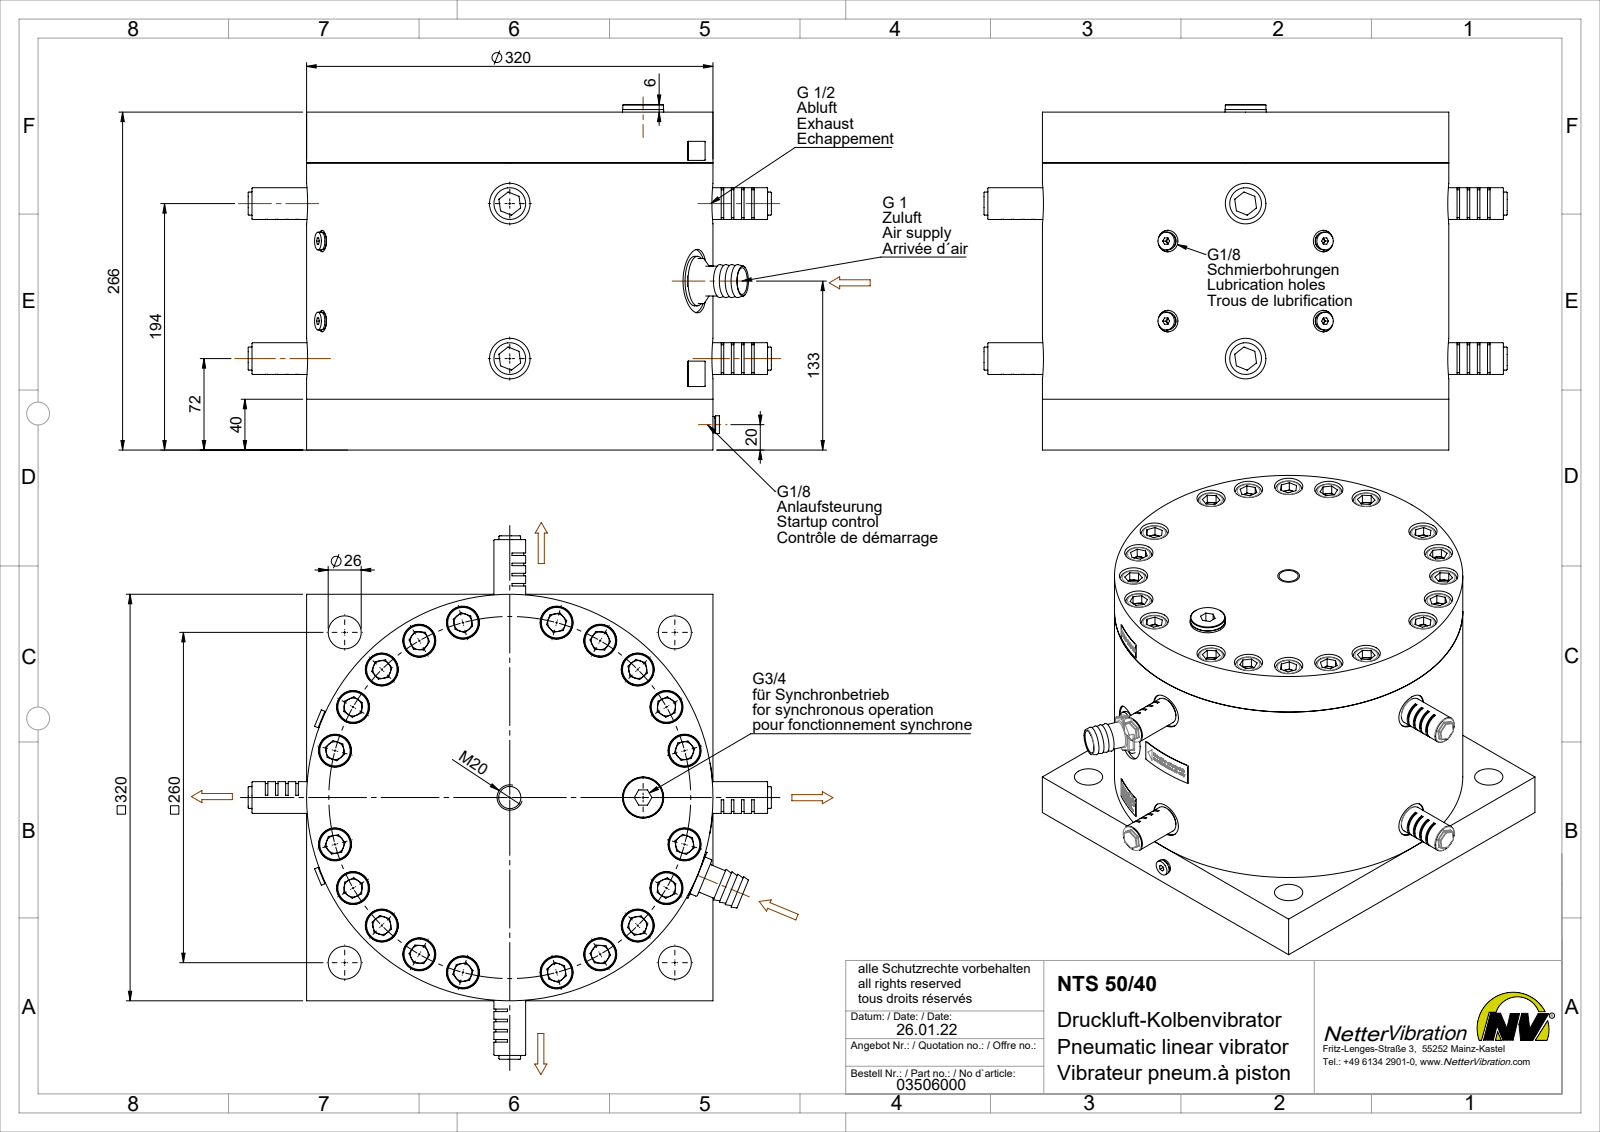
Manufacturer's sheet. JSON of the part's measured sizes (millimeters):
{"part_name": "NTS 50-40 Kolbenvibrator #03506000", "step_written_by": "SolidWorks 2015 (AUTOMOTIVE_DESIGN)", "units": "millimeters", "bodies": {"solids": 107, "faces": 7486, "planar": 5546, "cylindrical": 1250, "other": 690}, "overall_size": [412, 412, 272], "volume_mm3": 22040000, "surface_area_mm2": 1312000, "round_holes": [[17, 24], [26, 24], [14, 21], [2, 6], [10, 6], [6, 5], [8.57, 5], [18.63, 4], [32, 4], [17.5, 1], [21, 1], [24.12, 1]], "round_bosses_or_shafts": [[25.4, 20], [24, 20], [16, 20], [14, 5], [13, 5], [9.73, 5], [25, 4], [22, 4]], "partial_cylinders_radius": [[0.5, 156], [1, 18], [160.2, 1]], "face_to_face_distances": [186, 40, 226, 39, 225, 265, 1, 266, 320, 19], "hole_center_spacings": [142.5, 37.2, 109.06, 226.1, 263.3, 282.56, 73.76, 201.52]}
